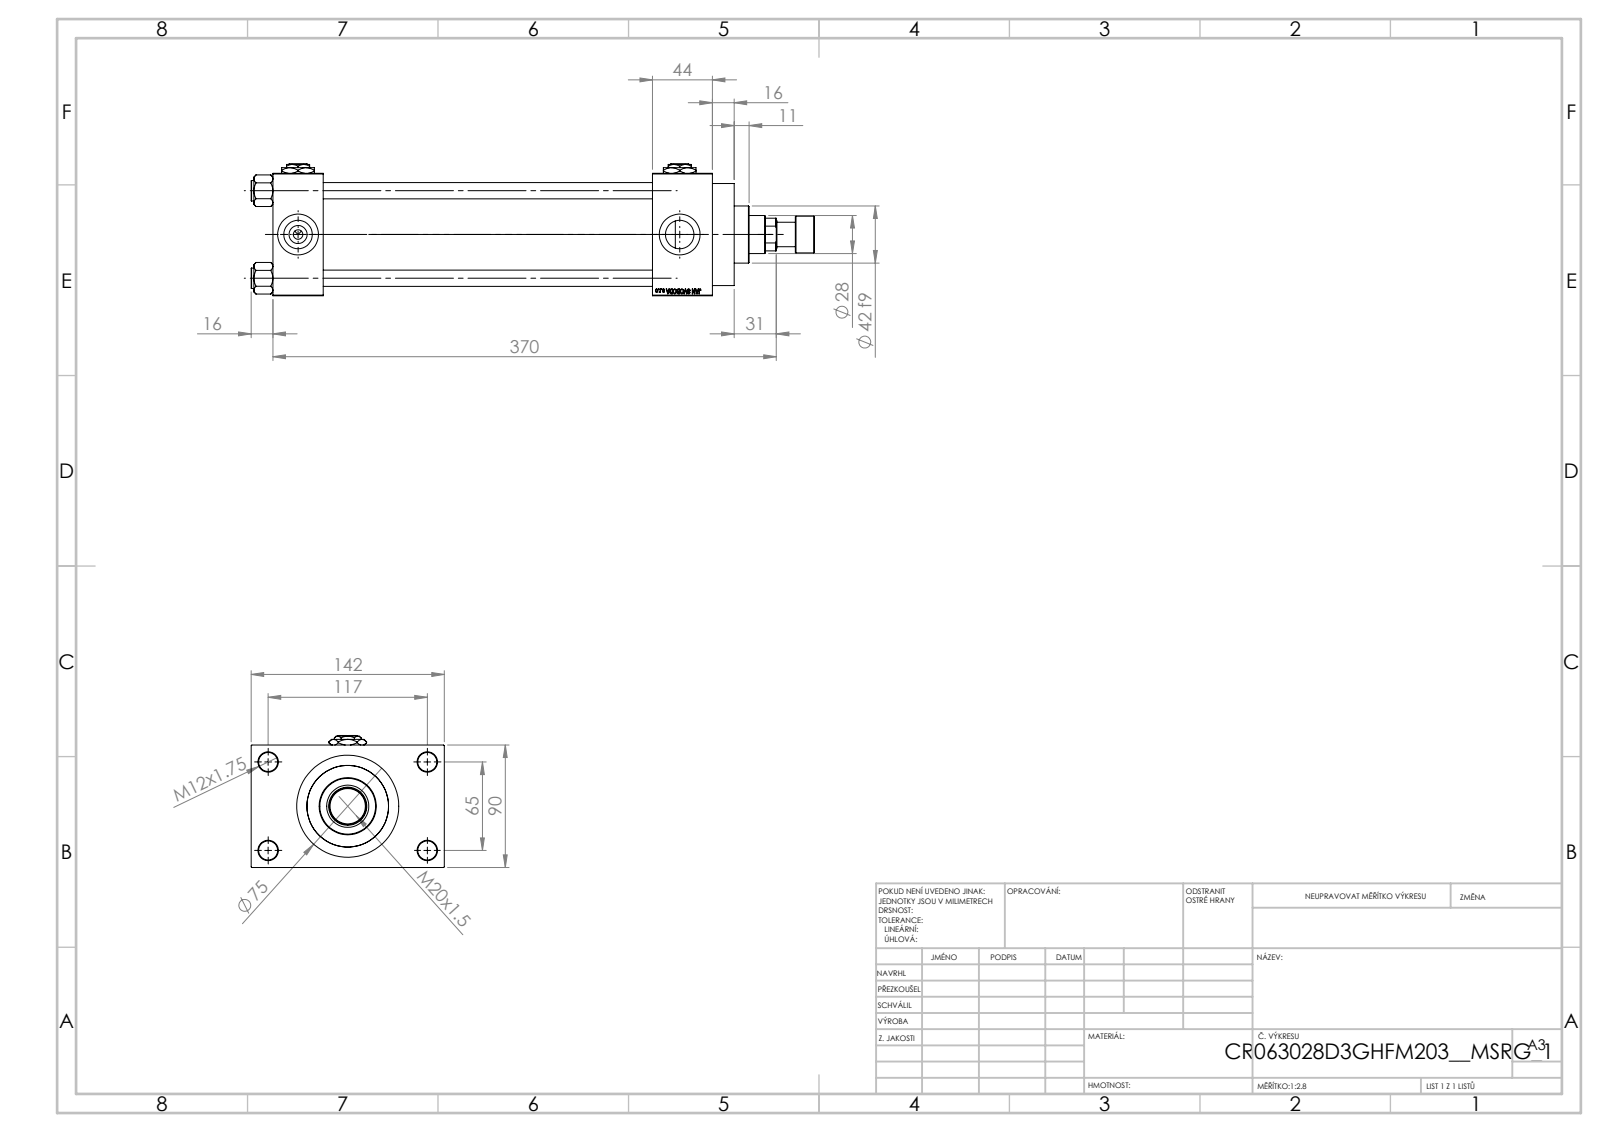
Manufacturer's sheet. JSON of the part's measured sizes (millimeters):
{"part_name": "V215CR_ROD_END_F; V215CR_D_Body; V215CR_VCP_D; NUT_M5_D (+3 more)", "step_written_by": "SolidWorks 2019 (CONFIG_CONTROL_DESIGN)", "units": "millimeters", "bodies": {"solids": 13, "faces": 1218, "planar": 549, "cylindrical": 103, "other": 566}, "overall_size": [414, 142, 97], "volume_mm3": 566024, "surface_area_mm2": 327523, "round_holes": [[12, 4], [14, 4], [20.96, 4], [30, 4], [7, 3], [18.5, 1], [28, 1], [31, 1], [50, 1], [60, 1], [63, 1]], "round_bosses_or_shafts": [[15, 4], [75, 1], [69, 1], [42, 1], [27, 1], [18, 1]], "face_to_face_distances": [90, 242, 37, 279, 286, 323, 44, 26, 116, 16], "hole_center_spacings": [26.35, 45.47, 64.3, 66.92, 69.81, 90.65, 111.34, 65]}
